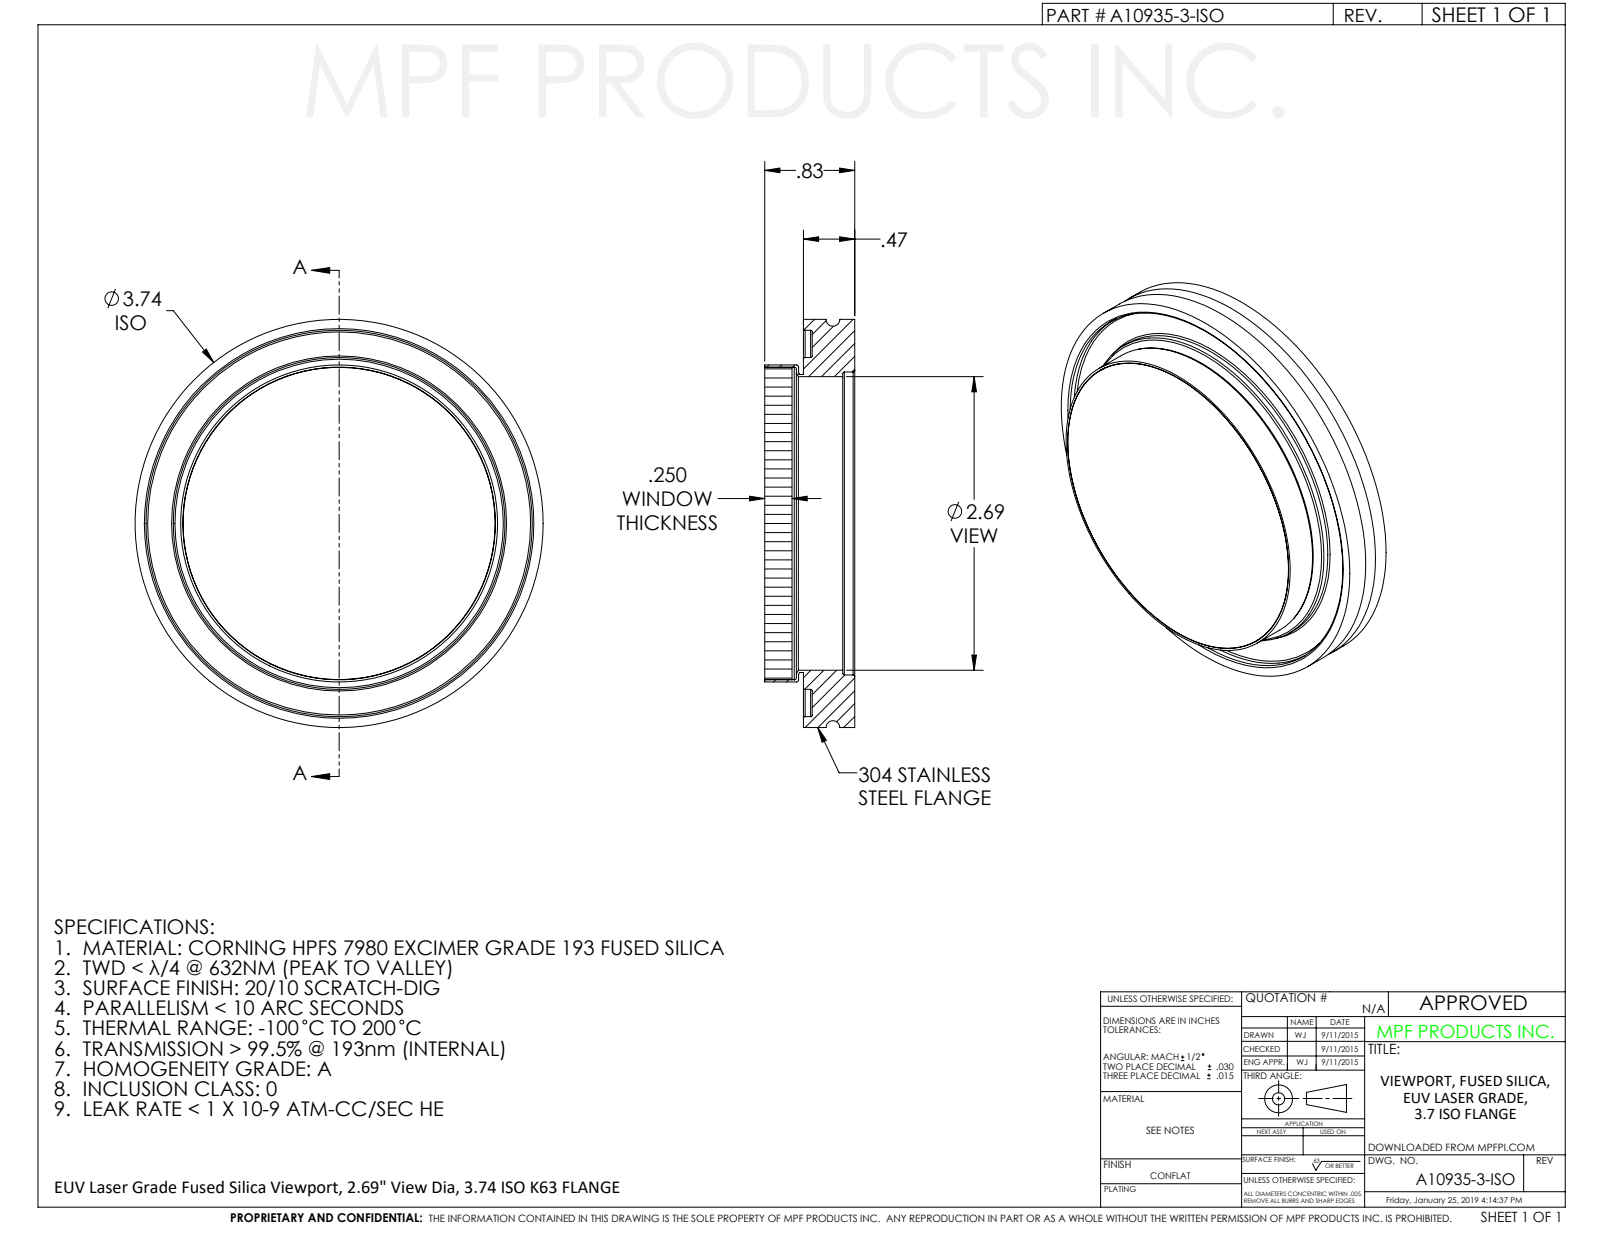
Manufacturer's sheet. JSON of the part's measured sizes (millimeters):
{"part_name": "A10935-3-ISO", "step_written_by": "SolidWorks 2012 (CONFIG_CONTROL_DESIGN)", "units": "millimeters", "bodies": {"solids": 1, "faces": 55, "planar": 11, "cylindrical": 22, "other": 22}, "overall_size": [95, 95, 22.2], "volume_mm3": 62810, "surface_area_mm2": 26350, "round_holes": [[68.3, 1], [69.2, 1], [70.5, 1], [72.3, 1], [89.9, 1]], "round_bosses_or_shafts": [[95, 1], [77.2, 1], [73.3, 1], [69.3, 1]], "face_to_face_distances": [6.4, 14.6, 21, 9, 9.9, 4.7, 11, 11.9, 2, 2.7]}
